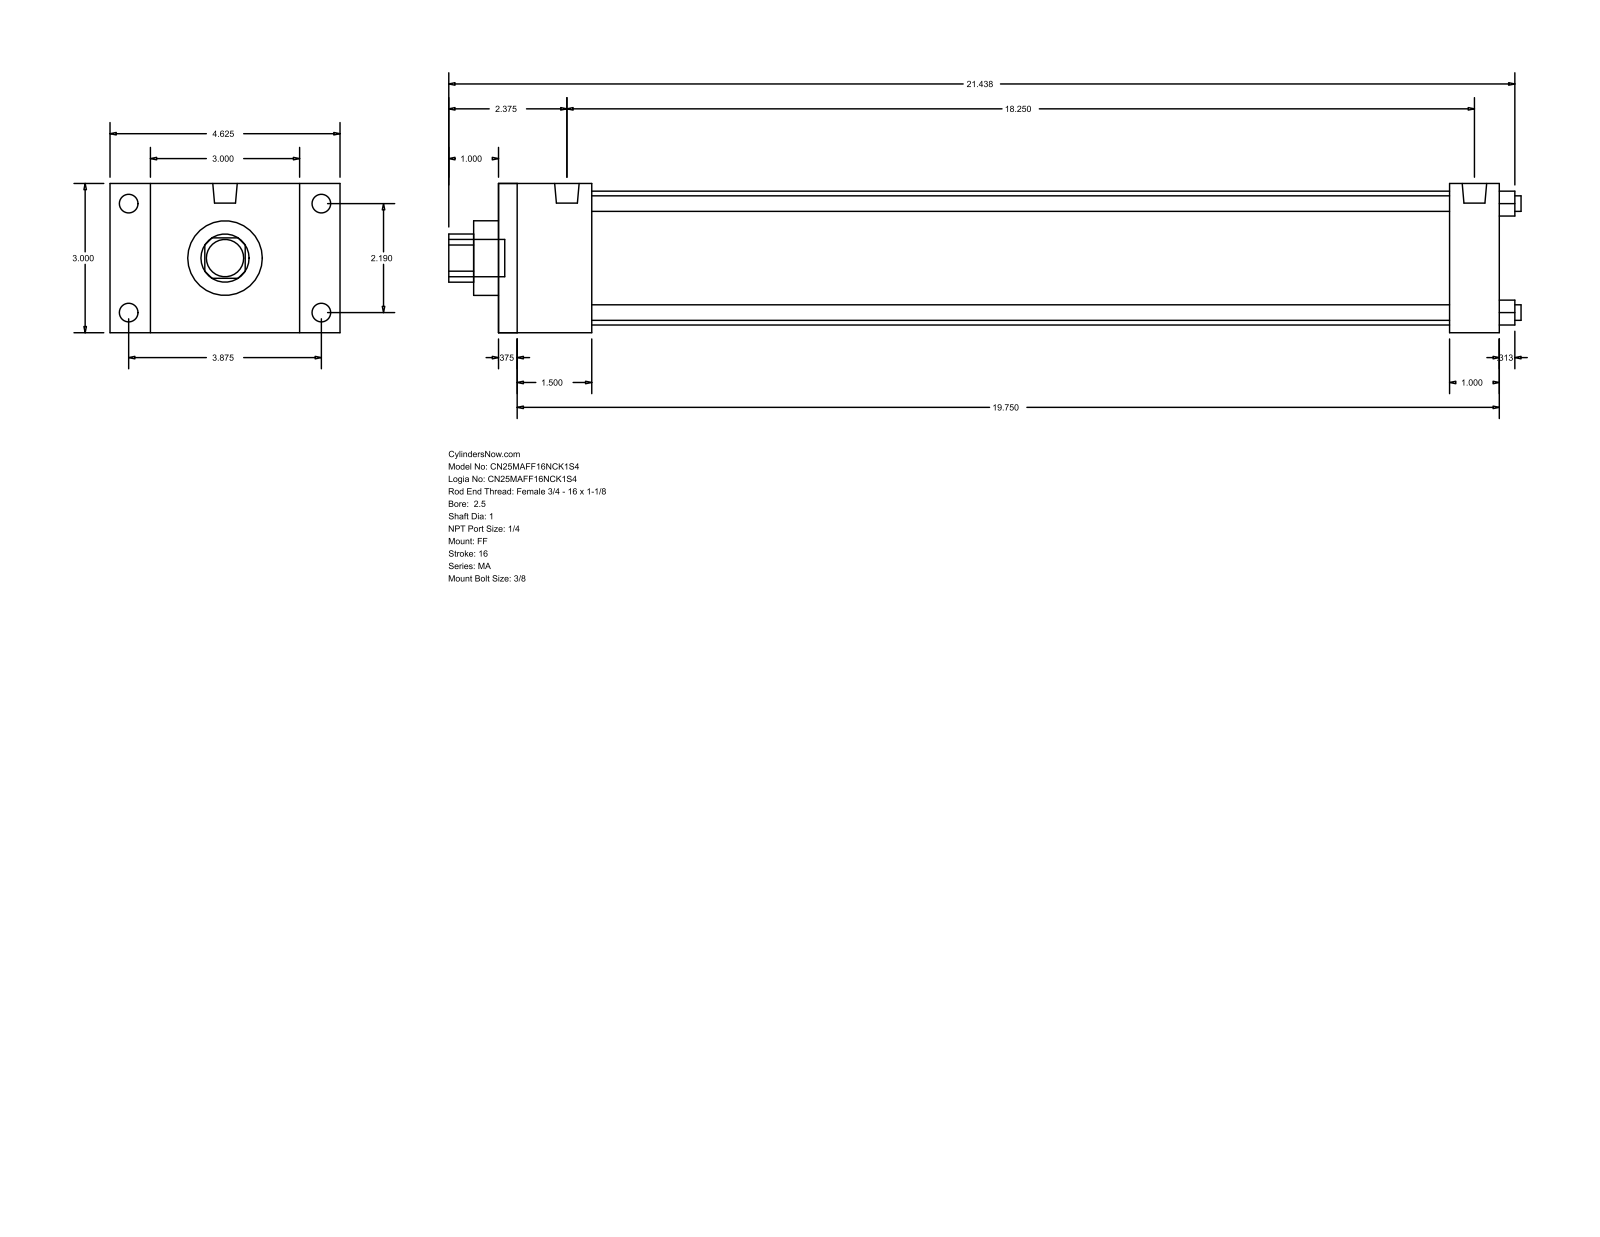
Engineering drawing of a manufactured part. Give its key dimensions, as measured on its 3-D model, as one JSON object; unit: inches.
{"part_name": "MA_FF__0250_1", "step_written_by": "GSSL Pune (CONFIG_CONTROL_DESIGN)", "units": "inches", "bodies": {"solids": 0, "faces": 92, "planar": 64, "cylindrical": 28, "other": 0}, "overall_size": [21.563, 4.625, 3], "round_holes": [[0.313, 4], [1, 1], [1.5, 1], [2.69, 1]], "round_bosses_or_shafts": [[0.375, 4], [0.313, 4], [0.492, 2], [0.75, 1]], "partial_cylinders_radius": [[0.484, 1]], "face_to_face_distances": [3, 20.125, 0.375, 19.75, 1, 1.875, 19.125, 1.5, 18.75, 17.25], "hole_center_spacings": [1.548, 2.19, 3.097]}
